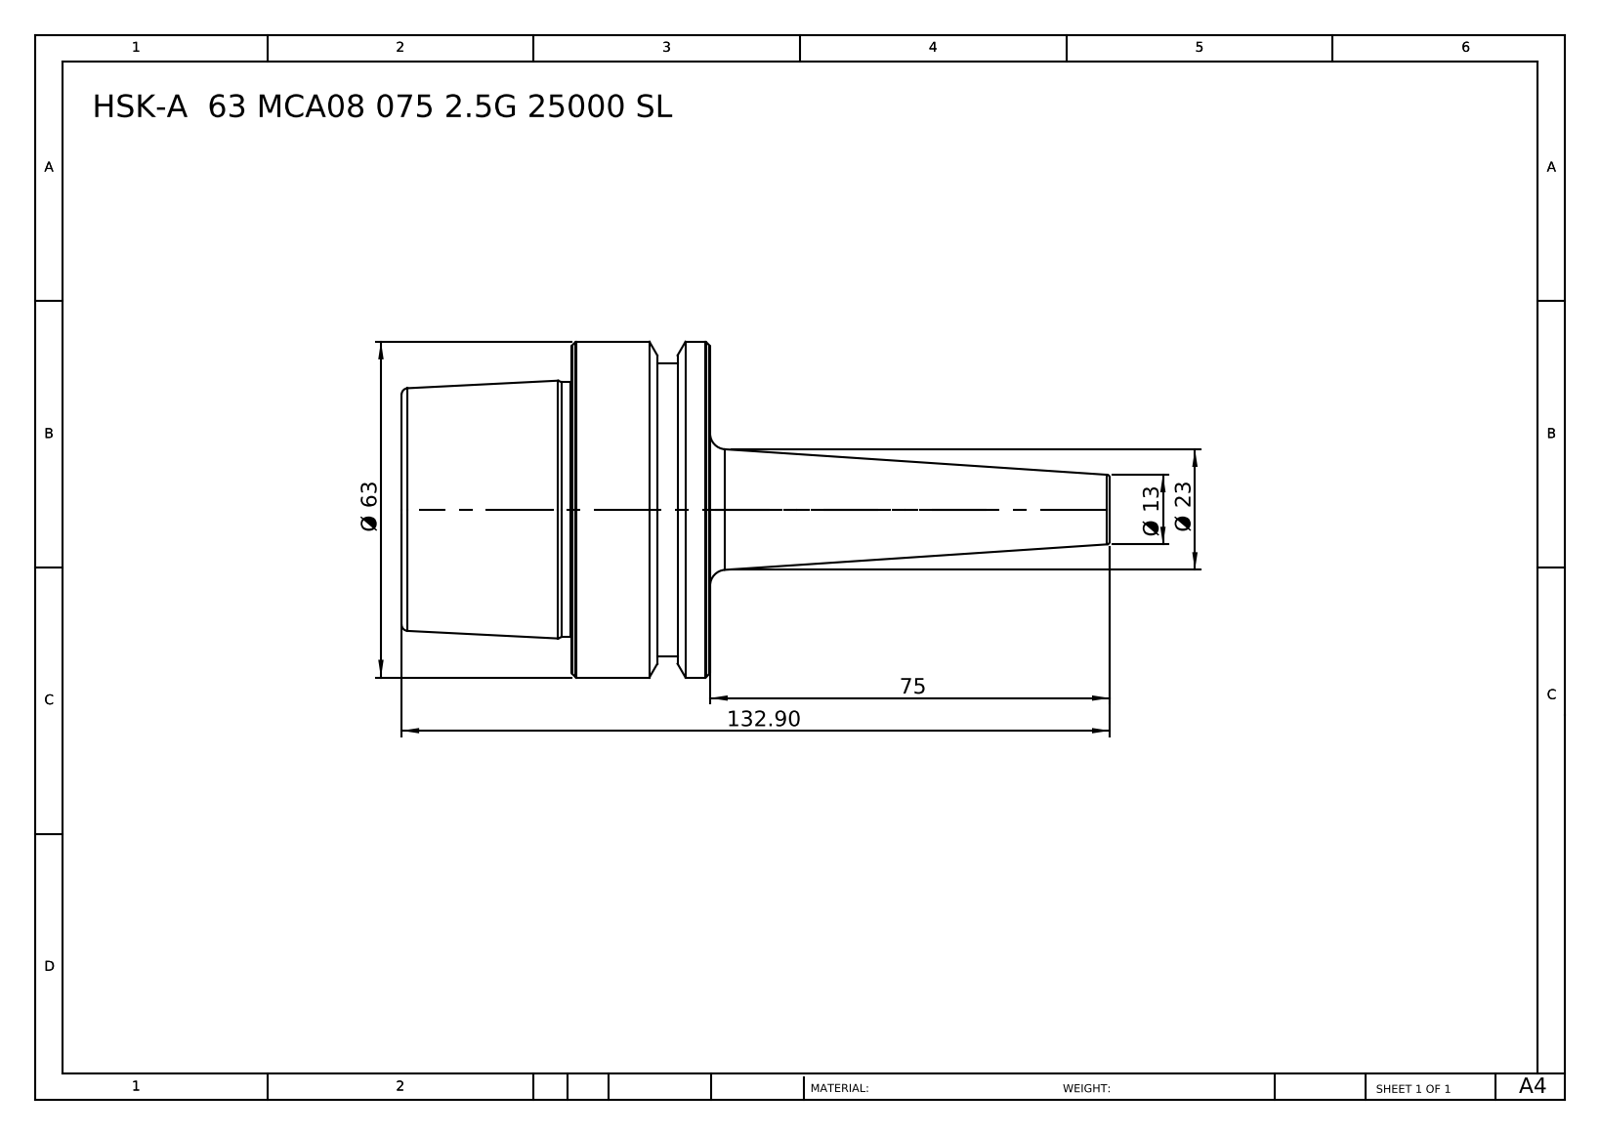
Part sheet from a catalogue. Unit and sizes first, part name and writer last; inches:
Units: inches
Overall size (bounding box): 5.232 × 2.48 × 2.48
Round bosses / shafts (diameter × count): ⌀2.48 ×1, ⌀2.165 ×1, ⌀1.881 ×1
Main face-to-face distances: 2.28, 1.024, 1.256, 0.24, 0.783, 2.039, 0.39, 0.15, 0.634, 1.89
Volume: 9.294 in³ · Surface area: 31.83 in²
Bodies: 1 solid, 46 faces (6 planar, 8 cylindrical, 32 other)
Part name (STEP PRODUCT): HSK-A 63 MCA08 075 2.5G 25000 SL
STEP written by: SolidWorks 2014 (CONFIG_CONTROL_DESIGN)
